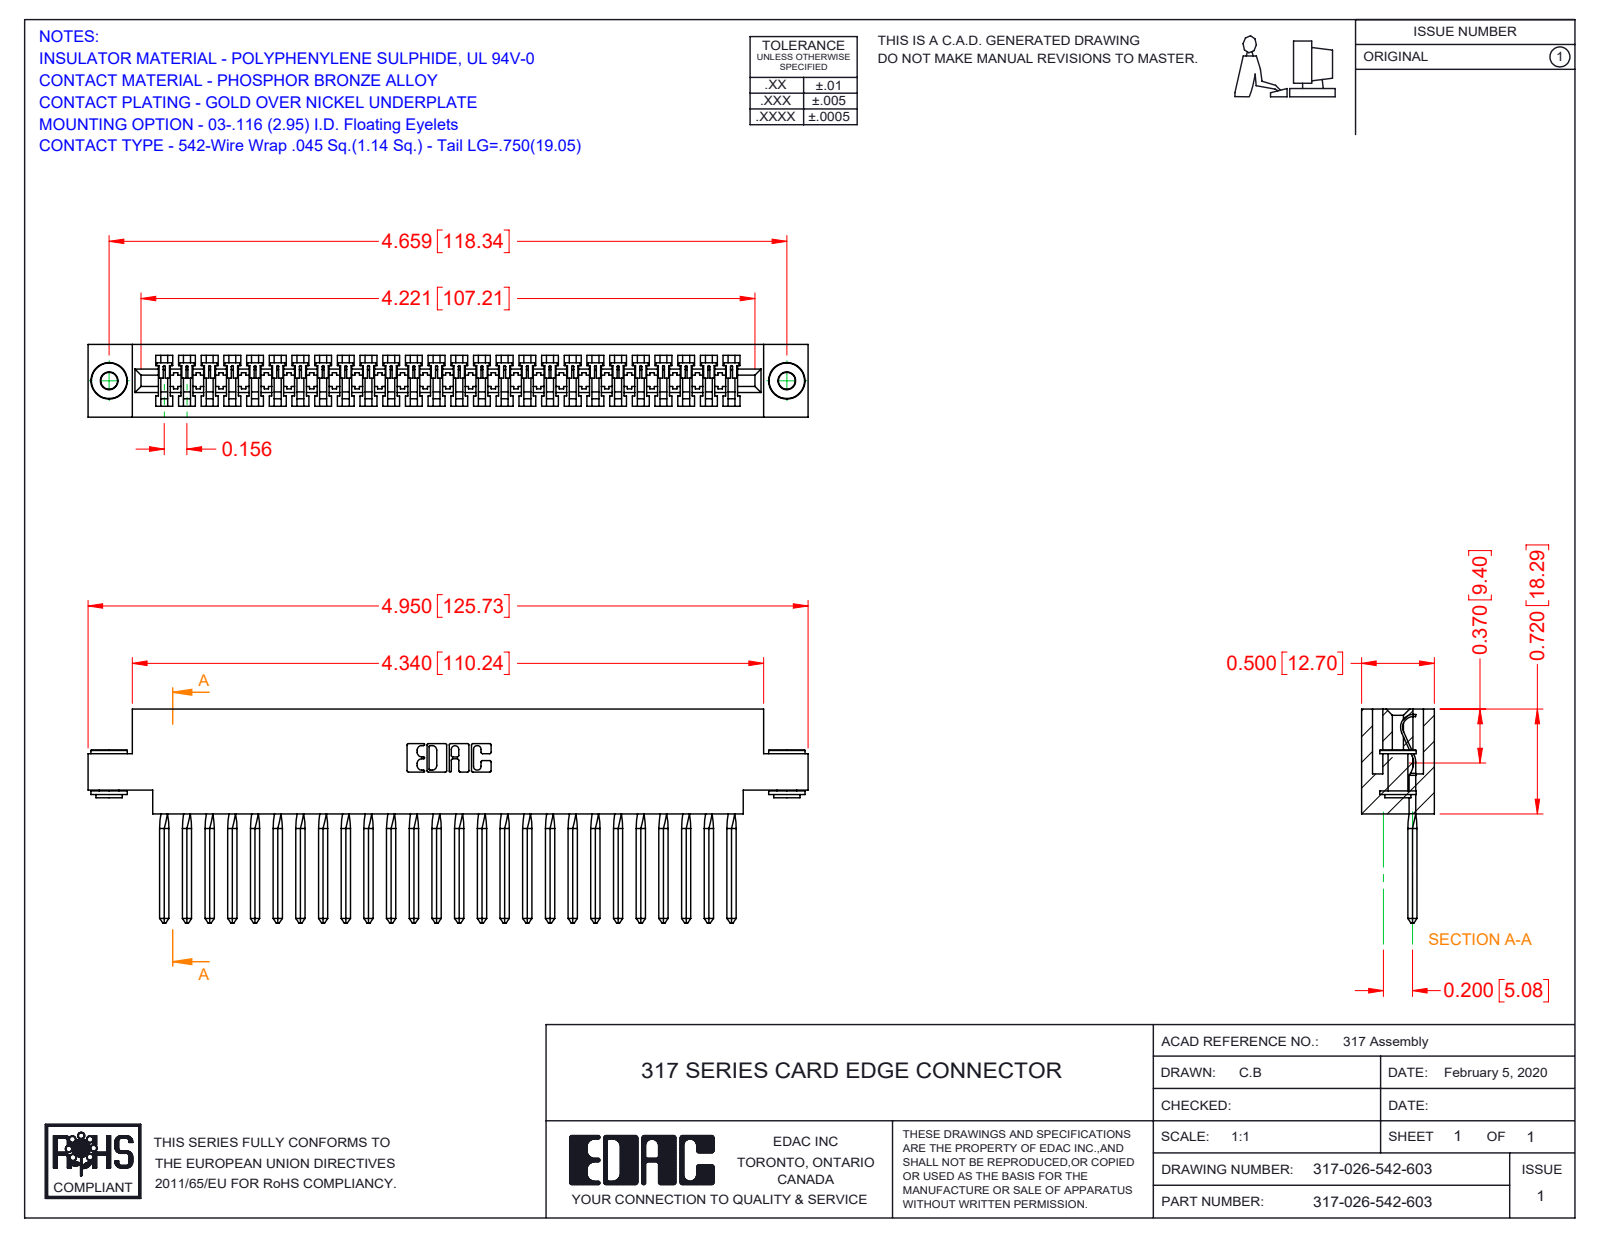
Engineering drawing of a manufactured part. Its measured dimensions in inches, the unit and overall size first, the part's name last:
Units: inches
Overall size (bounding box): 4.95 × 1.47 × 0.5
Round holes (diameter × count): ⌀0.116 ×2, ⌀0.156 ×2
Round bosses / shafts (diameter × count): ⌀0.25 ×2, ⌀0.18 ×2, ⌀0.136 ×2
Partial cylindrical surfaces — rounded edges, fillets, slot ends (radius × count): R0.006 ×52, R0.01 ×22, R0.007 ×6, R0.031 ×6, R0.026 ×3, R0.074 ×1, R0.089 ×1, R0.1 ×1
Main face-to-face distances: 0.5, 0.075, 0.425, 0.35, 0.11, 0.72, 0.136, 0.211, 0.289, 0.213
Hole centre spacings: 4.659
Volume: 1.16 in³ · Surface area: 35.74 in²
Bodies: 29 solids, 2090 faces (1732 planar, 246 cylindrical, 112 other)
Part name (STEP PRODUCT): 317-026-542-603; 317-290-003_542; 317 Part_.156 Dia - TH; 345-250-002_345-250-002-102
STEP written by: SolidWorks 2016 (CONFIG_CONTROL_DESIGN)
